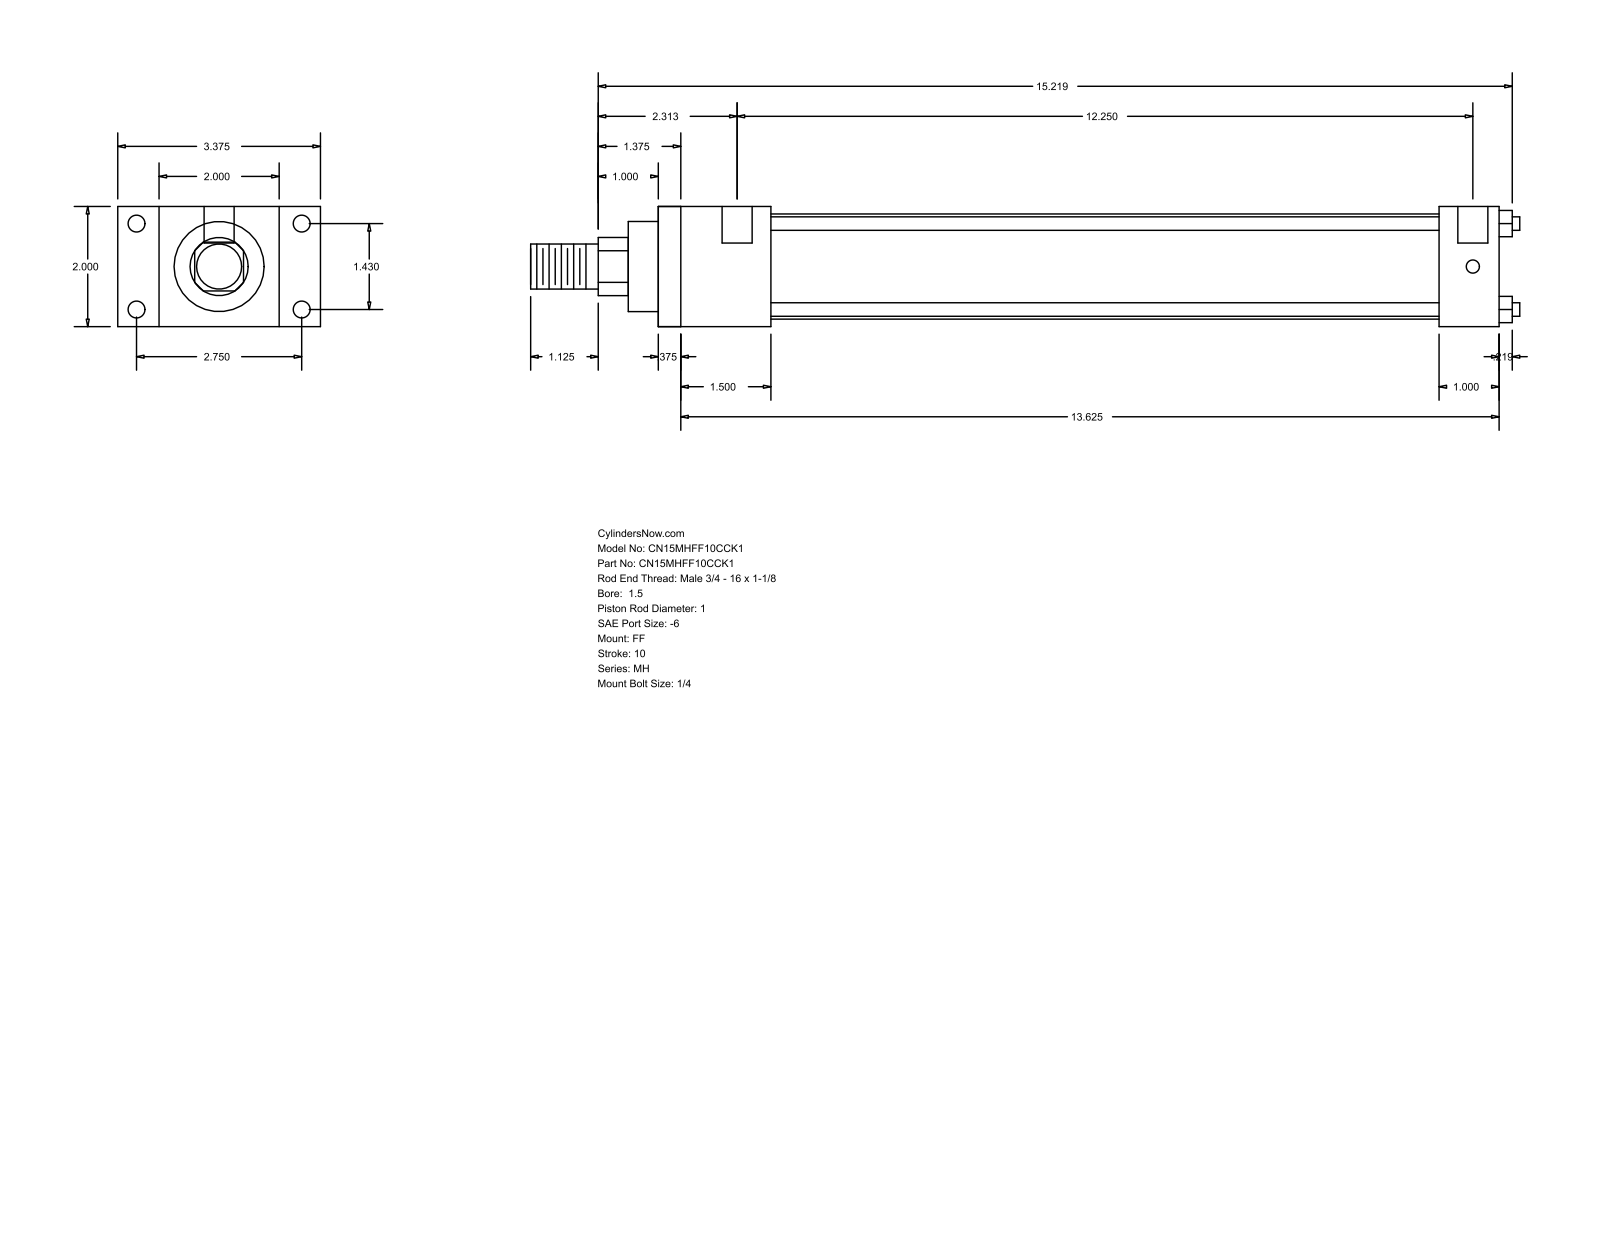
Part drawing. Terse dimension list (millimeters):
name: MH_FF__0150_1
written by: GSSL Pune (CONFIG_CONTROL_DESIGN)
unit: mm
bodies: 0 solids, 92 faces (64 planar, 28 cylindrical, 0 other)
size: 418.31 × 85.72 × 50.8
holes: 4× ⌀5.56, 4× ⌀7.14, 2× ⌀12.7
bosses: 4× ⌀5.71, 1× ⌀44.45, 1× ⌀38.1, 1× ⌀25.4, 1× ⌀19.05
rounds: 1× R12.29
face distances: 50.8, 355.6, 9.52, 346.08, 25.4, 17.46, 68.26, 47.63, 38.11, 307.97
hole spacings: 36.32, 69.84, 78.72, 314.33, 3.18, 311.15
